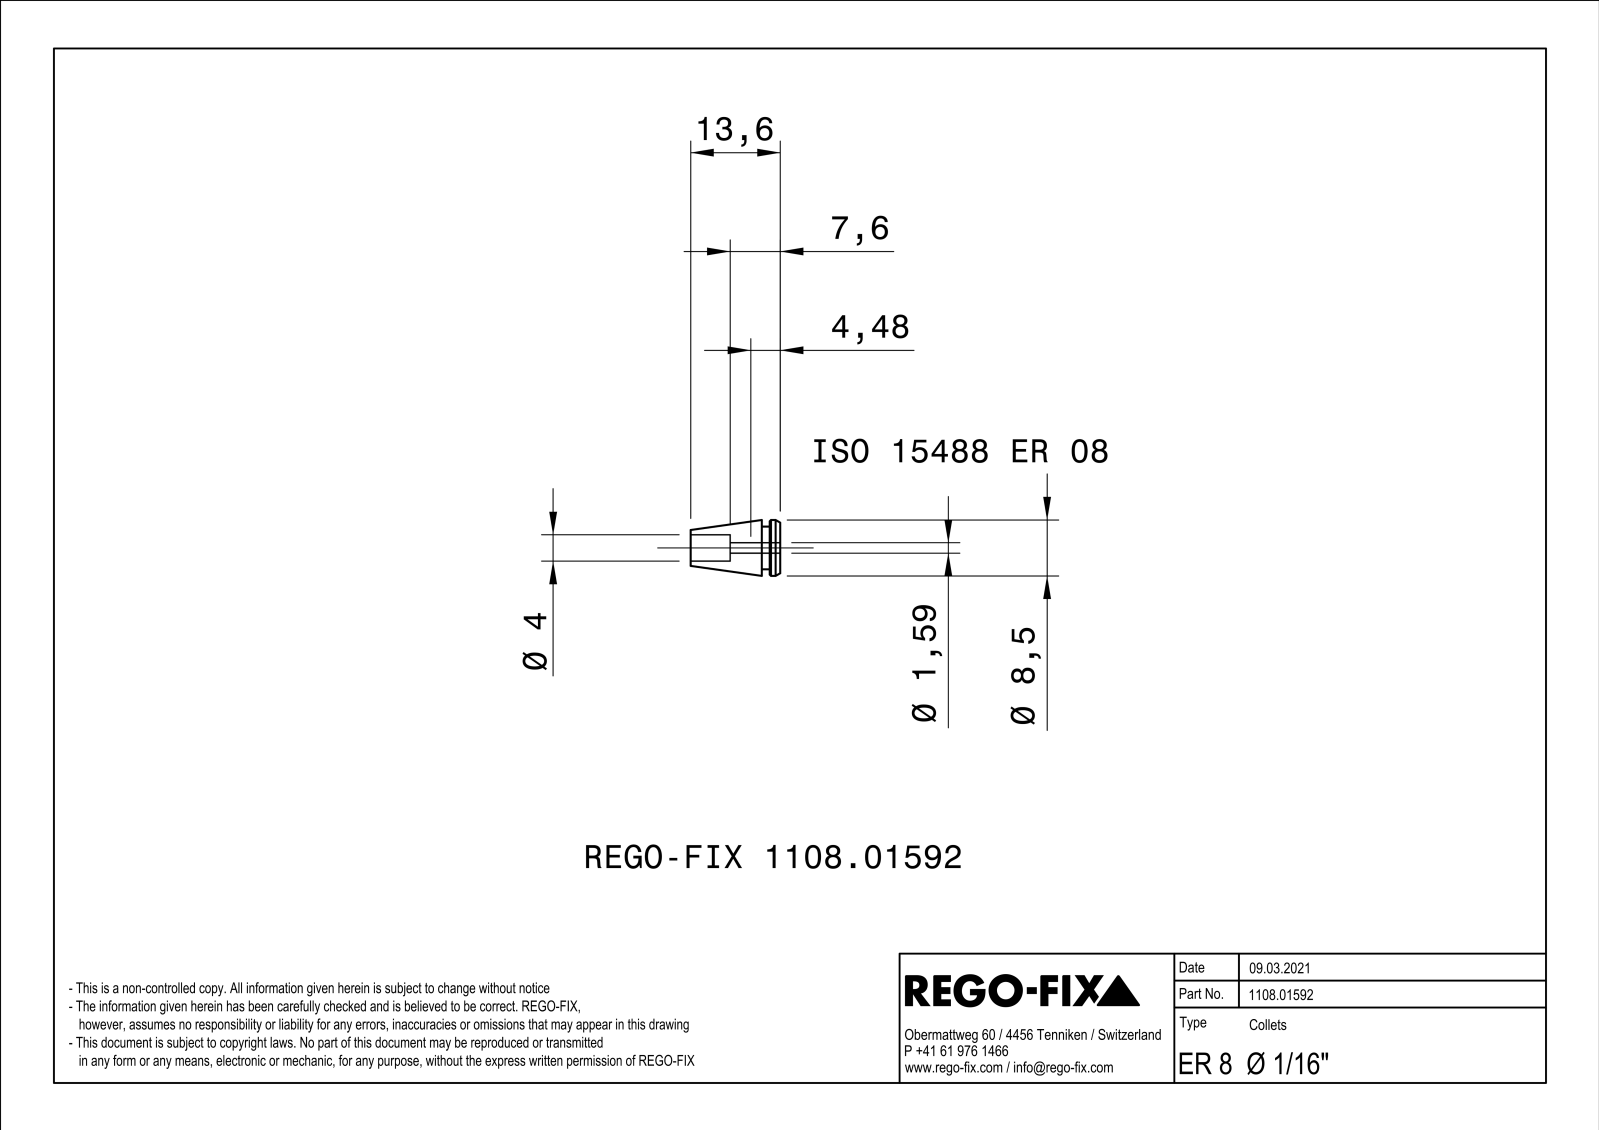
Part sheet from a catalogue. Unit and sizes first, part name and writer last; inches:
Units: inches
Overall size (bounding box): 0.535 × 0.334 × 0.334
Round holes (diameter × count): ⌀0.063 ×1
Round bosses / shafts (diameter × count): ⌀0.335 ×1
Partial cylindrical surfaces — rounded edges, fillets, slot ends (radius × count): R0.079 ×1, R0.128 ×1
Main face-to-face distances: 0.018, 0.018, 0.017, 0.11, 0.063, 0.047, 0.236, 0.299, 0.189, 0.535
Volume: 0.021 in³ · Surface area: 1.48 in²
Bodies: 1 solid, 202 faces (73 planar, 31 cylindrical, 98 other)
Part name (STEP PRODUCT): NOCUT
STEP written by: SIEMENS PLM Software Solid Edge ST10 (AUTOMOTIVE_DESIGN)
